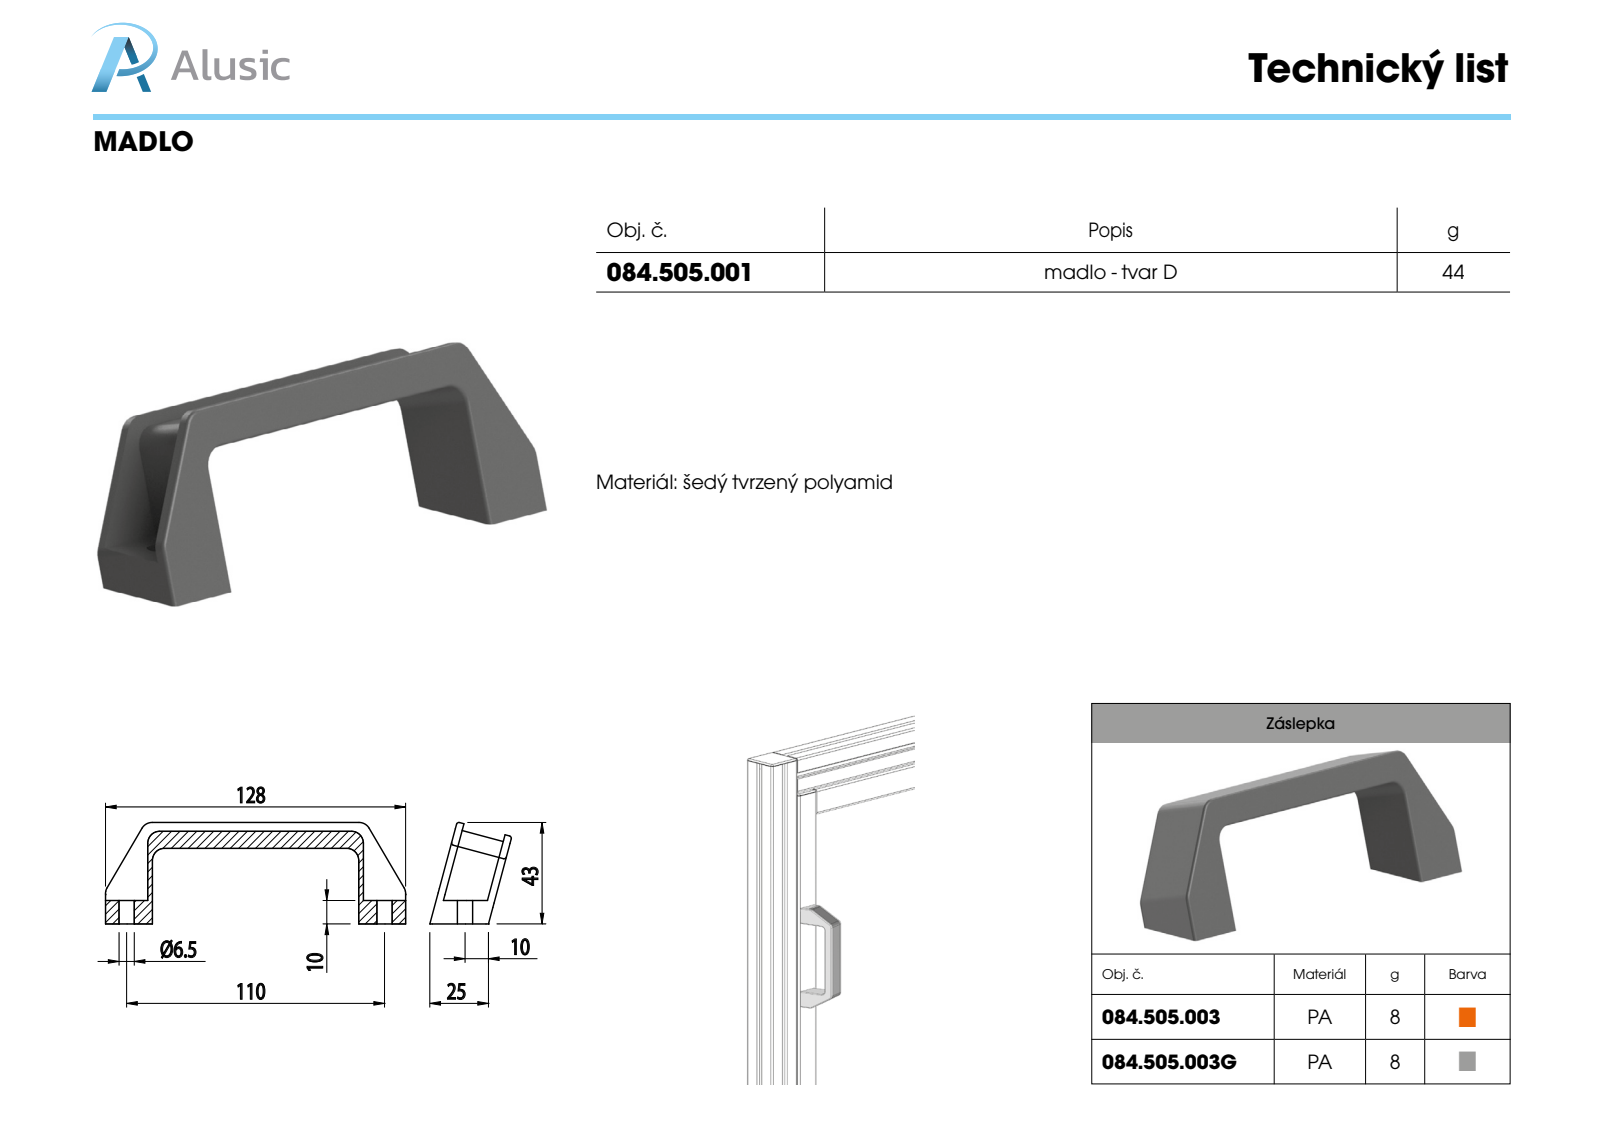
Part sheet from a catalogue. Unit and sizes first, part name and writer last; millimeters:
Units: millimetres
Overall size (bounding box): 128 × 43.27 × 34.76
Round holes (diameter × count): ⌀6.5 ×2
Partial cylindrical surfaces — rounded edges, fillets, slot ends (radius × count): R1 ×16, R5 ×12, R4 ×4
Main face-to-face distances: 1, 3.01, 21.15, 24.16, 9.05, 10.05, 3.02, 2.02, 7.03, 18.14
Hole centre spacings: 108
Volume: 35 370 mm³ · Surface area: 21 715 mm²
Bodies: 2 solids, 92 faces (36 planar, 44 cylindrical, 12 other)
Part name (STEP PRODUCT): 084.505.001
STEP written by: SolidWorks 2011 (CONFIG_CONTROL_DESIGN)
